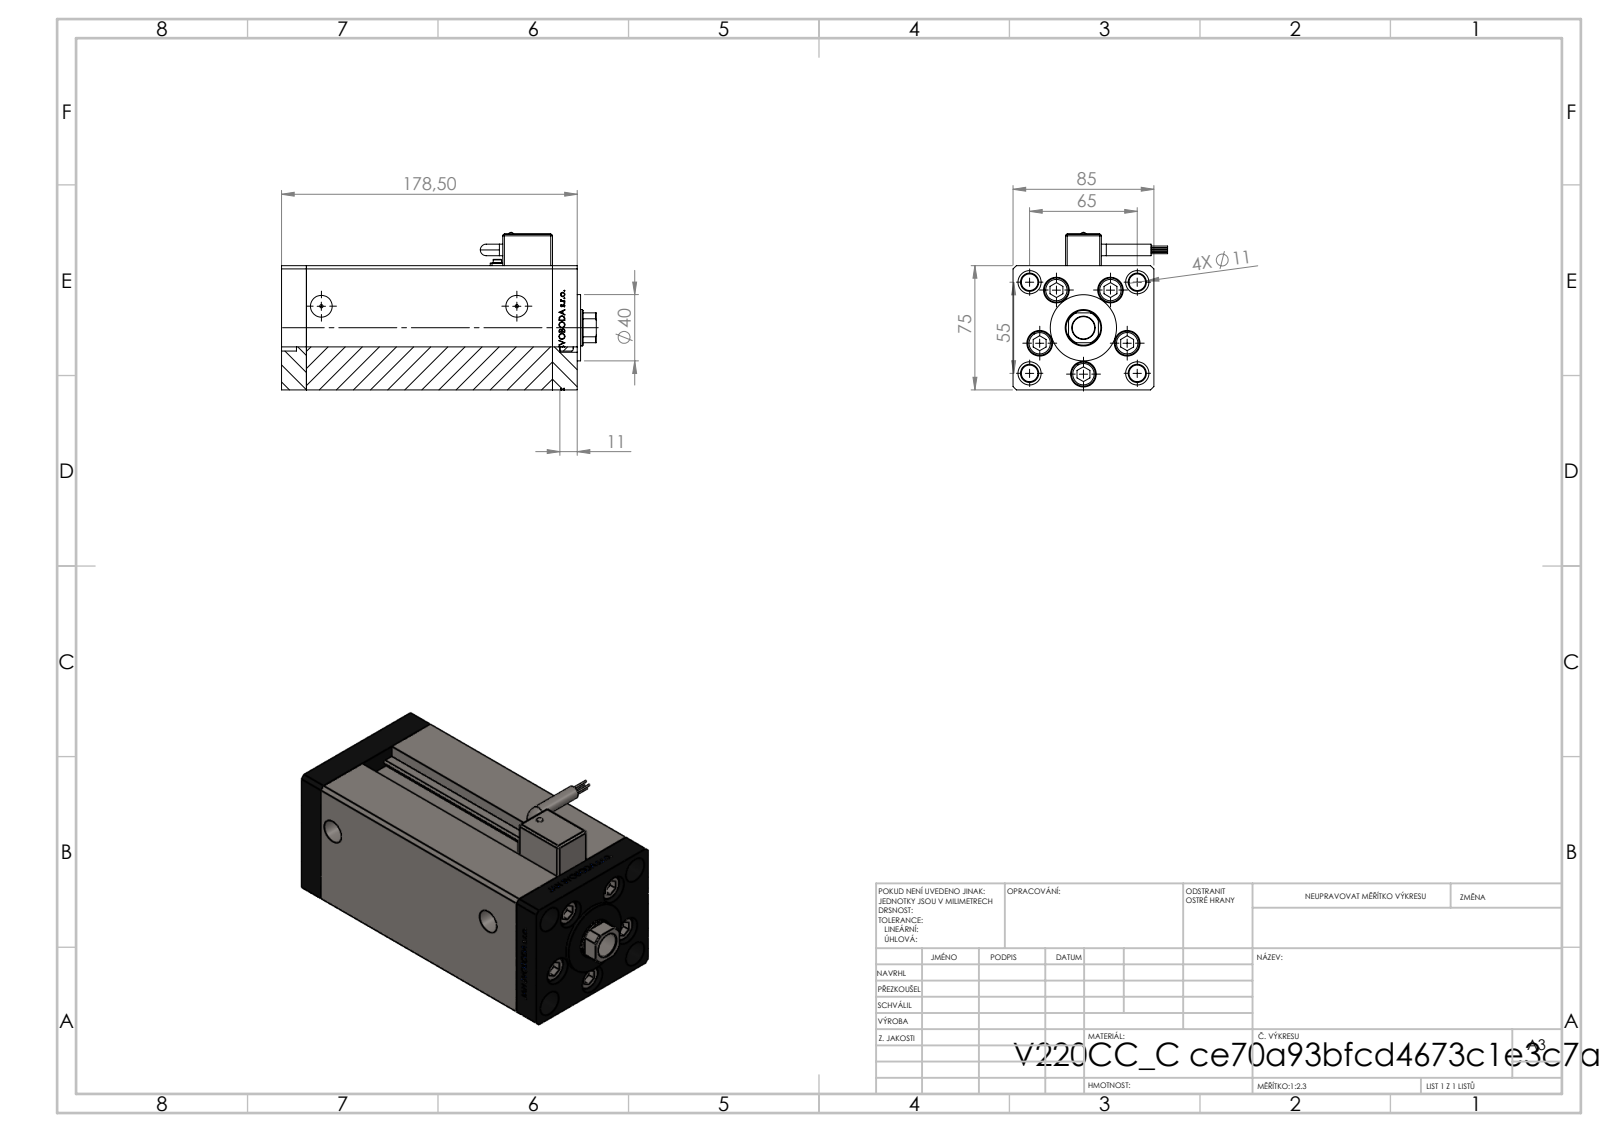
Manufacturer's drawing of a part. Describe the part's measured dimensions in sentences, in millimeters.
The part is named "V220C_C MIDDLE; Magnetic_Switch_MSU4; V220C_VC_C; V220C FRONT (+2 more)". Its 3-D file was written by "SolidWorks 2019 (CONFIG_CONTROL_DESIGN)". It is 14 solids with 1273 faces: 581 planar, 212 cylindrical and 480 other. Overall it measures 190 by 95.1 by 93.3 millimeters. Its volume is 964 221 cubic millimeters and its surface area 186 156 square millimeters. Round holes: 9 of diameter 11, 5 of diameter 15.5, 4 of diameter 10, 4 of diameter 14, 2 of diameter 2, 2 of diameter 13.16, 1 of diameter 3.6, 1 of diameter 5, 1 of diameter 7, 1 of diameter 13.5, 1 of diameter 14.5, 1 of diameter 22. Round bosses or shafts: 5 of diameter 8, 4 of diameter 14.5, 4 of diameter 0.85, 2 of diameter 7, 1 of diameter 40, 1 of diameter 6, 1 of diameter 3.5, 1 of diameter 2.5. Partial cylindrical surfaces (rounded edges, fillets, slot ends): 14 of radius 1, 2 of radius 0.93, 2 of radius 4, 1 of radius 10.5. The main face-to-face distances are 85, 75, 15, 148.5, 163.5, 10.5, 178.5, 34.25, 68.5, 144.25. The hole center spacings are 28, 42.57, 16.86, 19.17, 32.33, 32.5, 33.63, 37.33.
